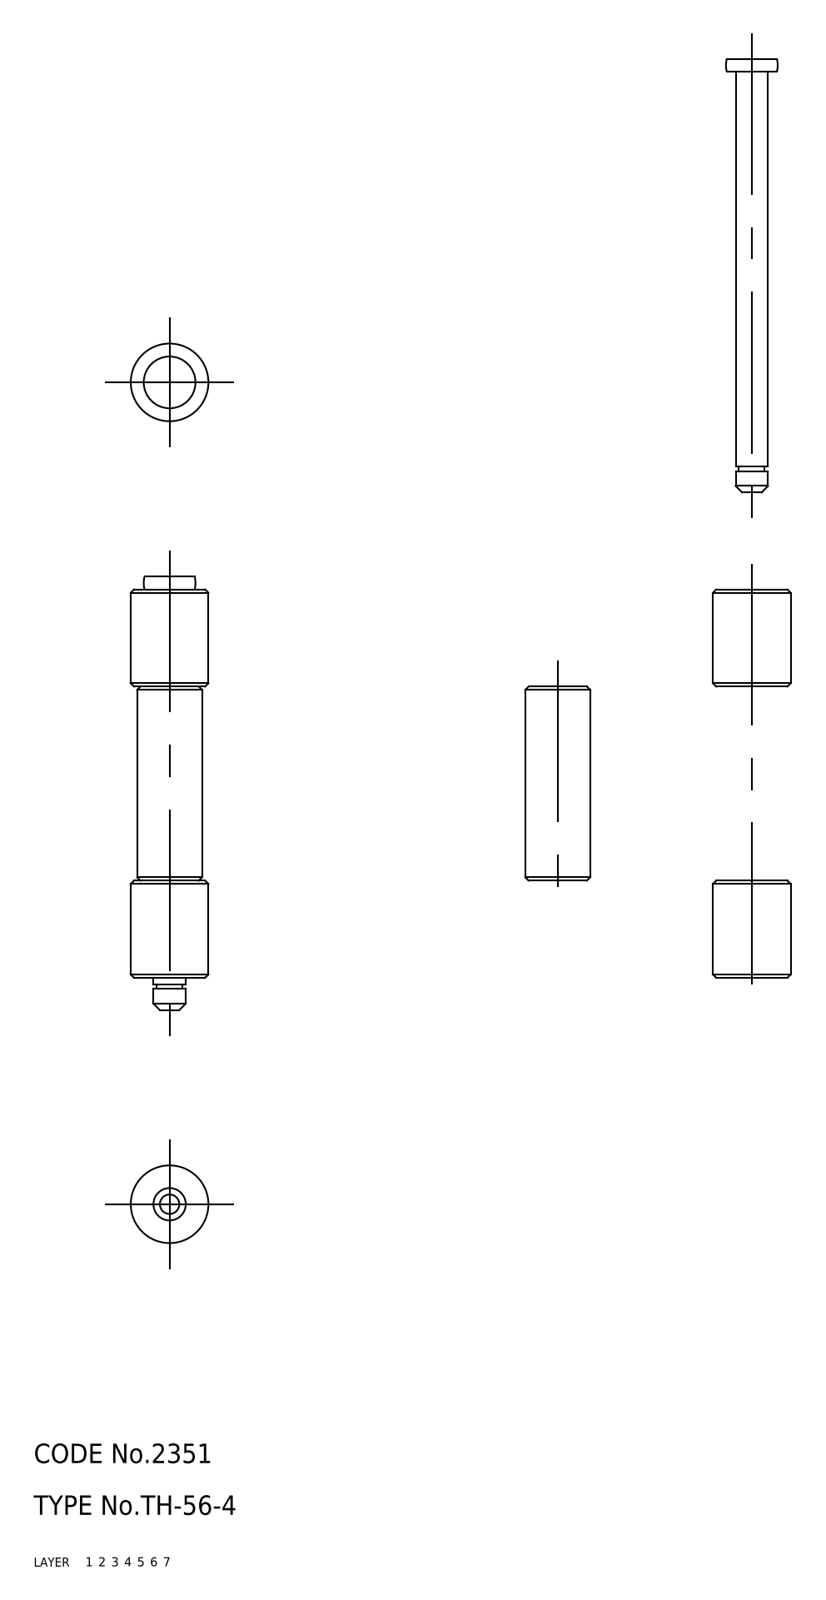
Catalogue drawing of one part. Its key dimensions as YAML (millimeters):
part_name: "collar_A; shaft; collar_B; TH_56_4_11524_36"
step_written_by: "CADfix (AUTOMOTIVE_DESIGN)"
units: millimeters
bodies: {solids: 4, faces: 44, planar: 0, cylindrical: 0, other: 44}
overall_size: [67, 12, 12]
volume: 5919
surface_area: 4612
